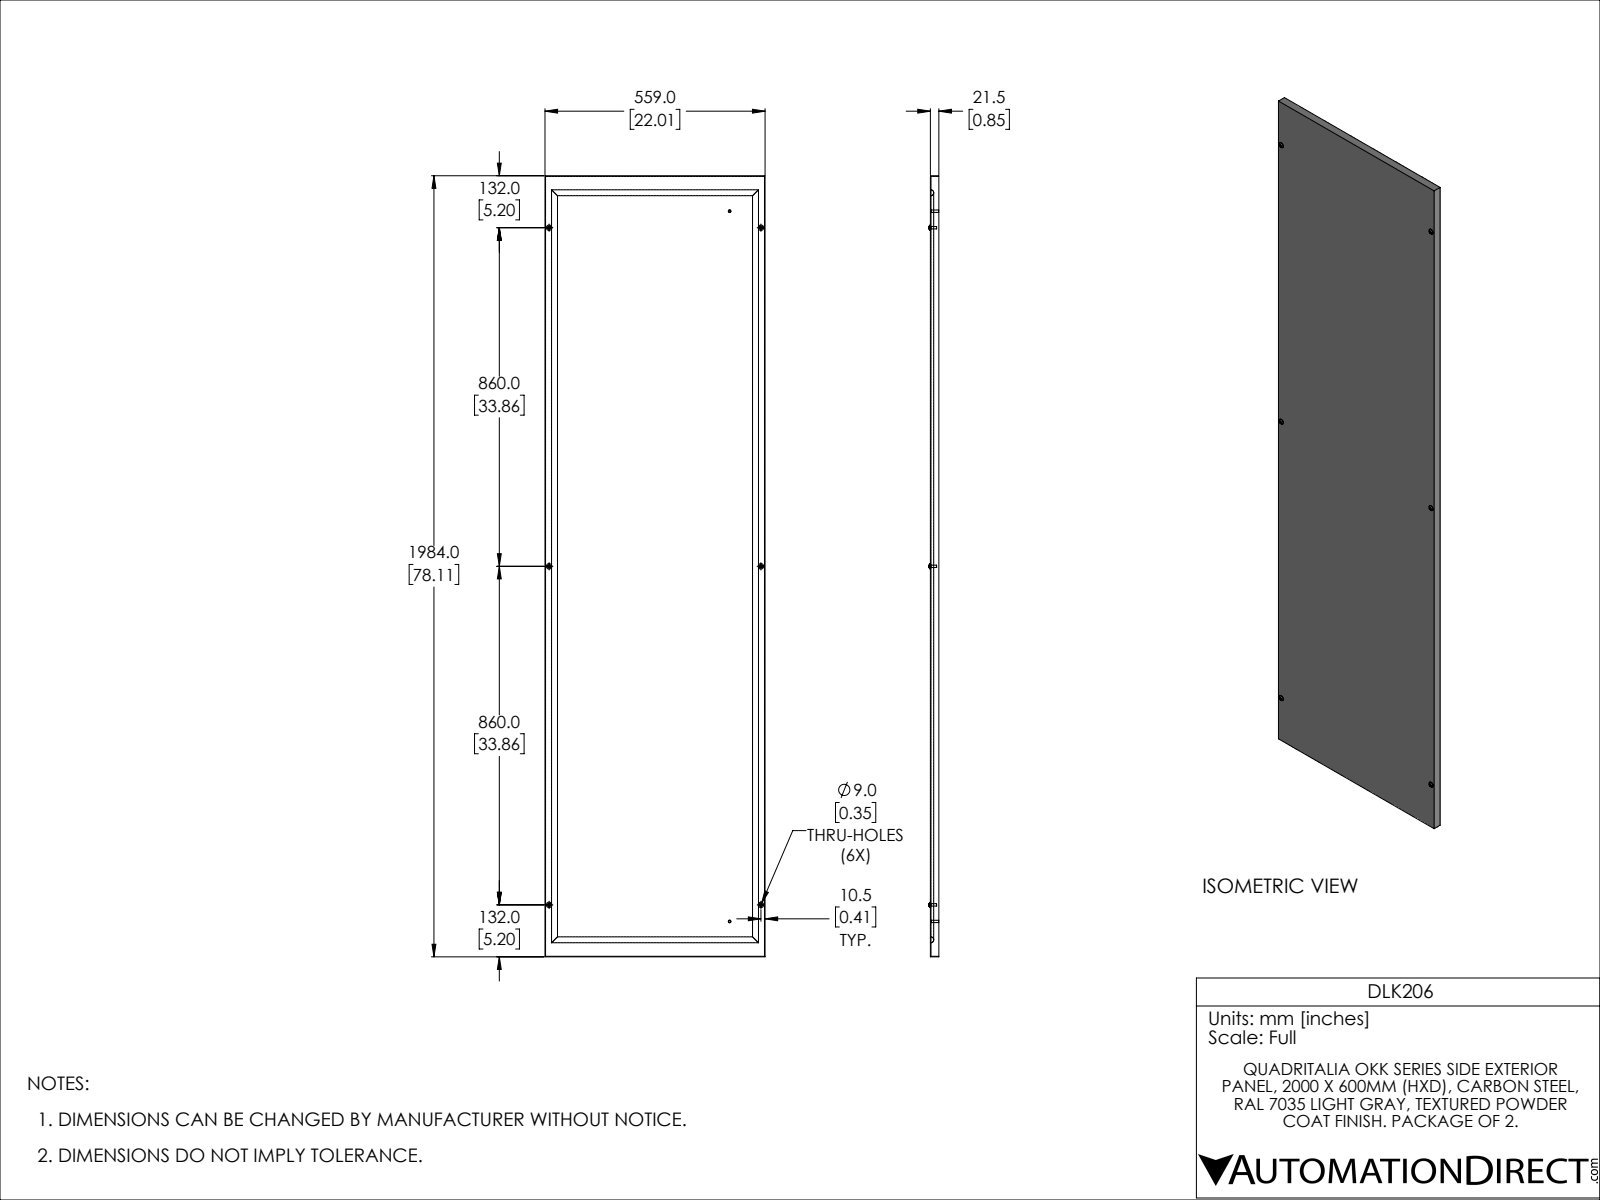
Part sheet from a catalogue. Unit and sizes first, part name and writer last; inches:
Units: inches
Overall size (bounding box): 78.11 × 22.008 × 0.992
Round holes (diameter × count): ⌀0.354 ×6
Round bosses / shafts (diameter × count): ⌀0.236 ×8, ⌀0.551 ×6, ⌀0.276 ×2
Partial cylindrical surfaces — rounded edges, fillets, slot ends (radius × count): R0.02 ×72, R0.296 ×4
Main face-to-face distances: 0.059, 21.949, 22.008, 21.89, 78.051, 78.11, 77.992, 0.846, 0.787, 38.606
Hole centre spacings: 33.858, 39.938, 21.181, 67.717, 70.952
Volume: 134.9 in³ · Surface area: 4 054 in²
Bodies: 13 solids, 243 faces (125 planar, 98 cylindrical, 20 other)
Part name (STEP PRODUCT): DLK206
STEP written by: SolidWorks 2021 (CONFIG_CONTROL_DESIGN)
